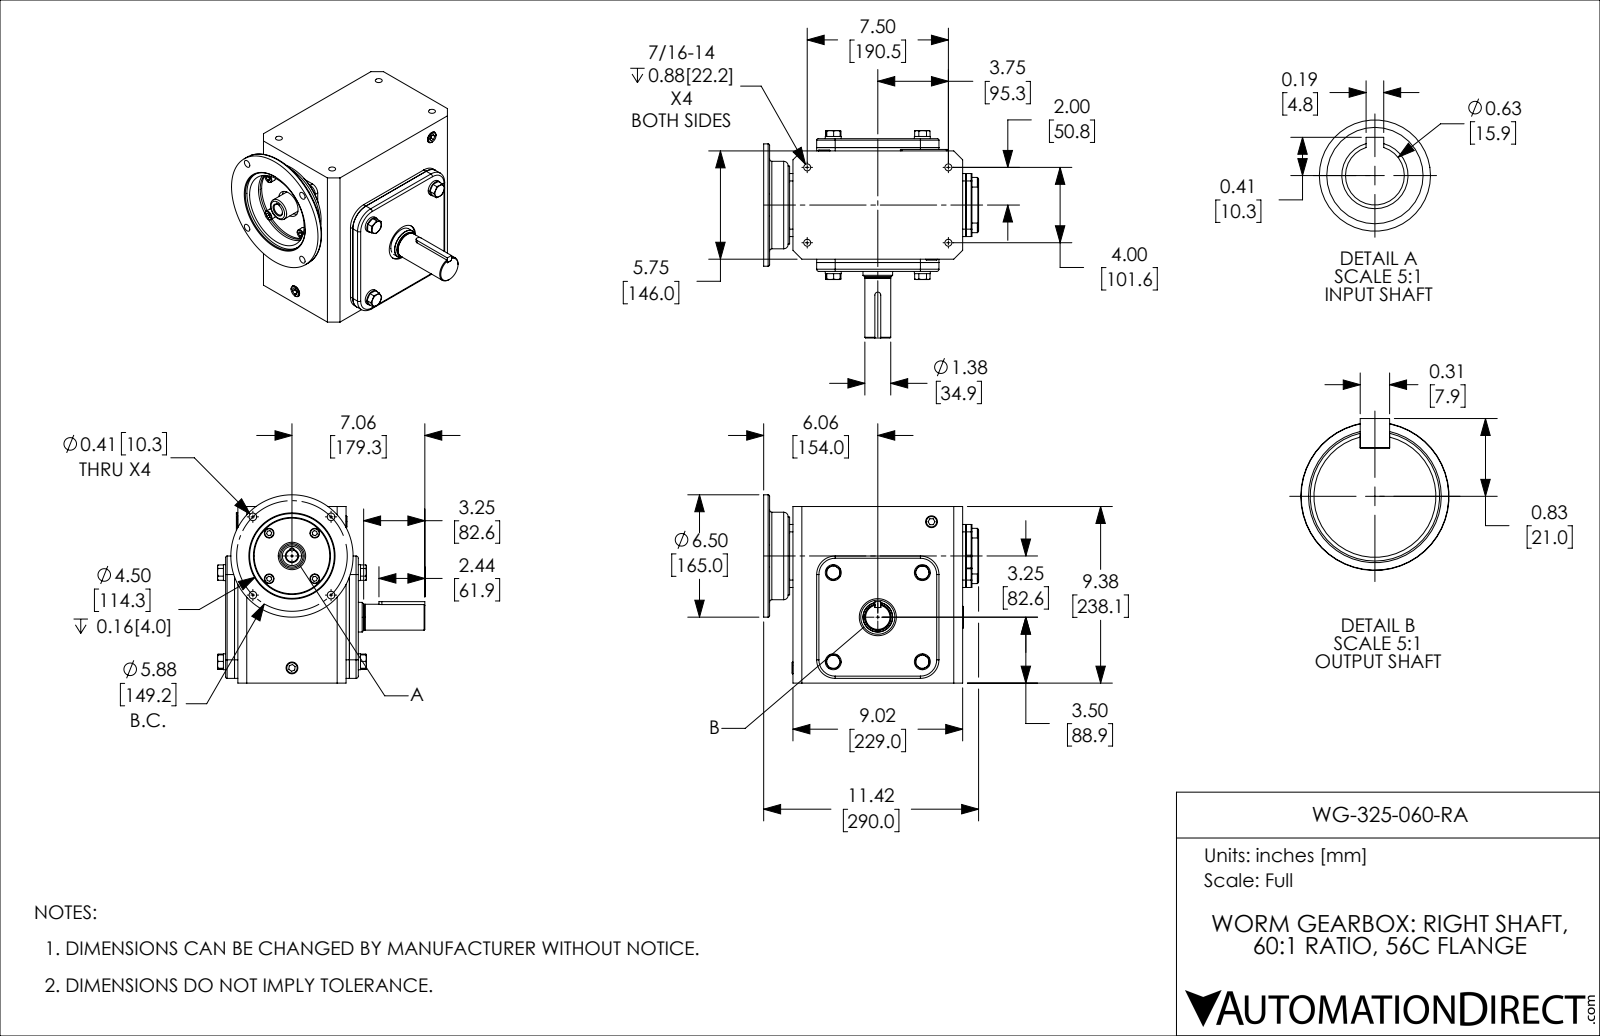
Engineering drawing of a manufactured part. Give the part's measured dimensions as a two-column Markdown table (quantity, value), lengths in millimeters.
| quantity | value |
| --- | --- |
| part name | WG-325-060-RA |
| STEP written by | SolidWorks 2017 (AUTOMOTIVE_DESIGN) |
| units | millimeters |
| bodies | 39 solids, 576 faces (318 planar, 168 cylindrical, 90 other) |
| overall size | 290 × 279.8 × 253.9 |
| volume | 8 251 000 mm³ |
| surface area | 578 800 mm² |
| round holes (diameter × count) | 9.3 × 4, 10.3 × 4, 16 × 3, 15 × 1, 15.9 × 1, 24.8 × 1, 30 × 1, 37 × 1, 50 × 1, 62 × 1, 70 × 1, 102 × 1 |
| round bosses / shafts (diameter × count) | 21.5 × 4, 13 × 4, 165 × 1, 118 × 1, 105 × 1, 72 × 1, 40 × 1, 34.9 × 1 |
| partial cylindrical surfaces (radius × count) | 2 × 11, 3 × 4, 10 × 4, 23 × 4, 25 × 4, 0.5 × 2, 1 × 2, 4 × 1 |
| main face-to-face distances | 2, 4.5, 165, 10, 177, 12, 167, 162.5, 14.5, 16.5 |
| hole center spacings | 74.6, 105.5, 60.6, 101.6, 111.5, 145.2, 147.8, 149.2 |
